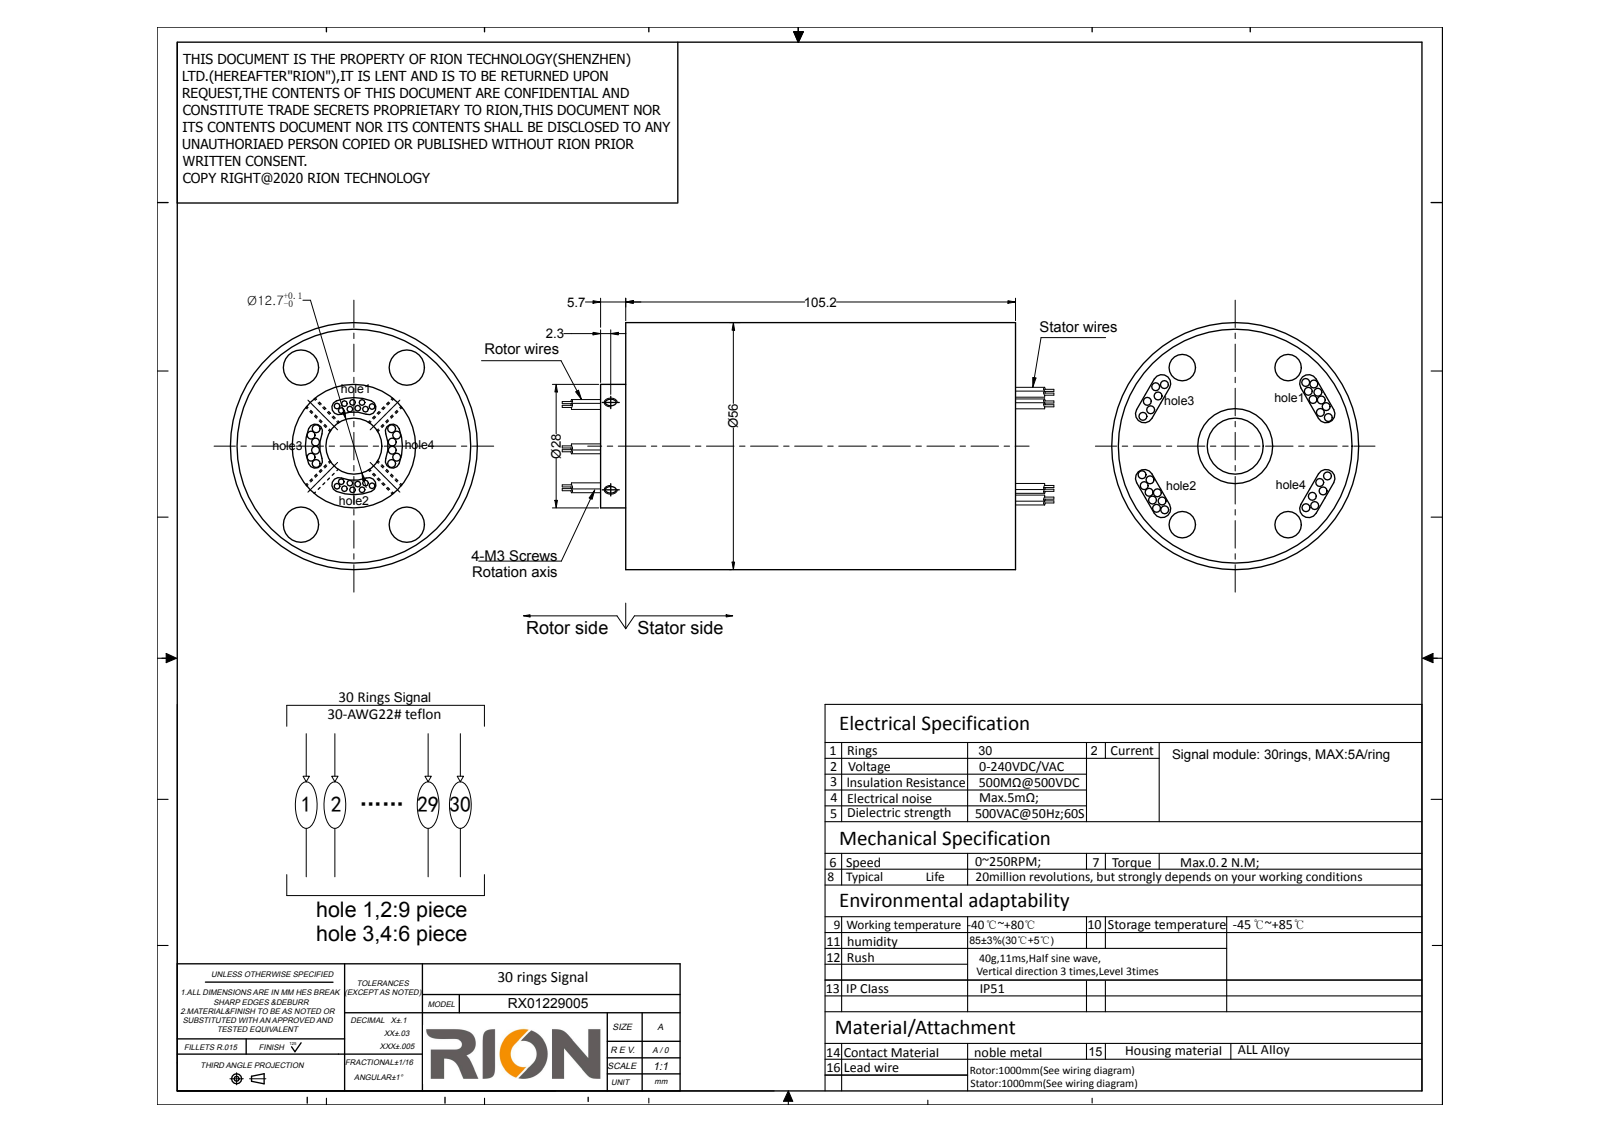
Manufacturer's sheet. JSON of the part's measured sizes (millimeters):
{"step_written_by": "SolidWorks 2014 (CONFIG_CONTROL_DESIGN)", "units": "millimeters", "bodies": {"solids": 1, "faces": 265, "planar": 85, "cylindrical": 180, "other": 0}, "overall_size": [129.4, 56, 56], "volume_mm3": 248944, "surface_area_mm2": 32673, "round_holes": [[2.5, 2], [12.7, 1], [15.8, 1], [53, 1]], "round_bosses_or_shafts": [[1.3, 60], [56, 1], [52.9, 1], [28, 1], [15.5, 1]], "partial_cylinders_radius": [[1.62, 8], [2, 8], [8.12, 1], [11.38, 1]], "face_to_face_distances": [105.2, 5.7, 110.9, 109.9, 104.2, 1, 10, 119.4, 0.5, 5.2]}
